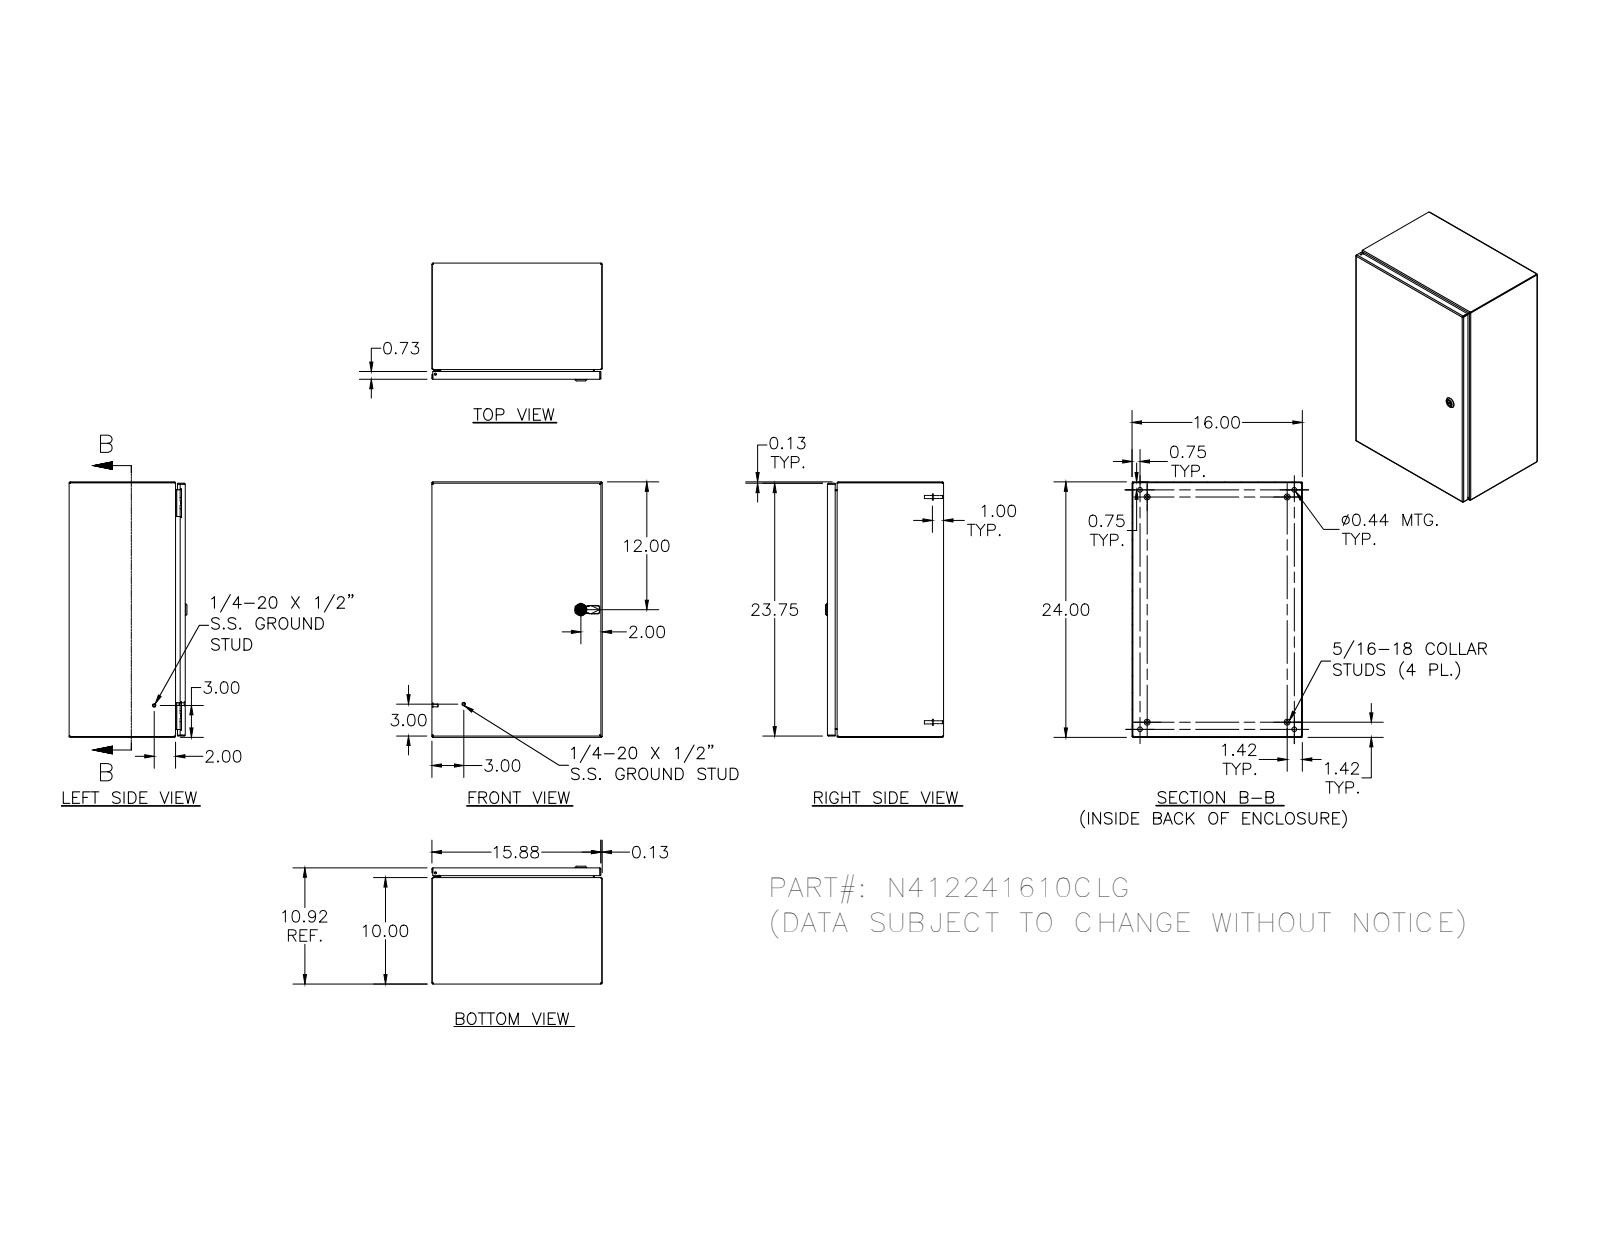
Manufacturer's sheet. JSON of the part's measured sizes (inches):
{"part_name": "N412241610CLG", "step_written_by": "SolidWorks 2018 (AUTOMOTIVE_DESIGN)", "units": "inches", "bodies": {"solids": 33, "faces": 1449, "planar": 530, "cylindrical": 547, "other": 372}, "overall_size": [24, 16, 11.075], "volume_in3": 128, "surface_area_in2": 3479, "round_holes": [[0.188, 5], [0.093, 4], [0.152, 4], [0.167, 4], [0.172, 4], [0.437, 4], [0.156, 2], [0.187, 1], [0.197, 1], [0.315, 1], [0.394, 1], [0.402, 1]], "round_bosses_or_shafts": [[0.25, 10], [0.563, 4], [0.36, 4], [0.32, 4], [0.3, 4], [0.256, 4], [0.164, 4], [0.131, 4]], "partial_cylinders_radius": [[0.012, 30], [0.031, 30], [0.05, 26], [0.105, 20], [0.016, 18], [0.125, 16], [0.02, 13], [0.032, 8]], "face_to_face_distances": [0.074, 10.843, 0.074, 10.769, 10.917, 15.926, 15.852, 15.926, 16, 23.852], "hole_center_spacings": [20, 0.66, 0.656, 1.307, 1.965, 0.5, 0.984, 1.311]}
